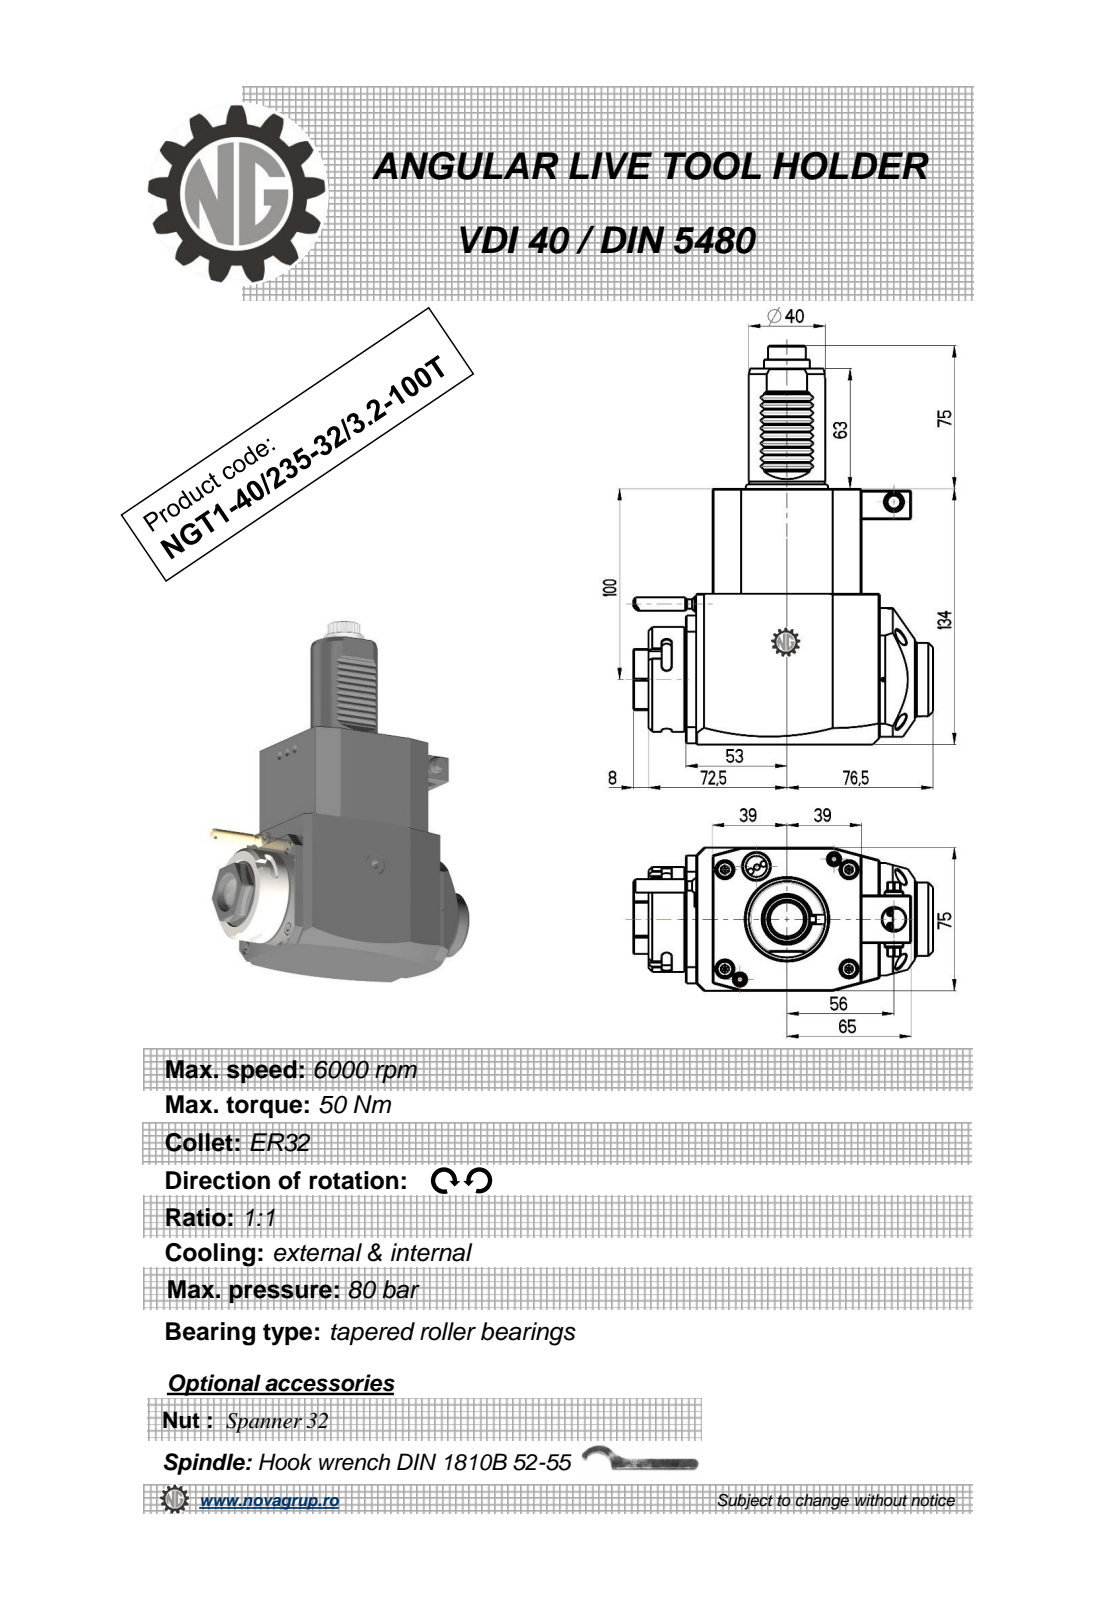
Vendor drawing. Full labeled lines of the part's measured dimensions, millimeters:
Part name (STEP PRODUCT): NGT1_40_235_32_3_2_100T
STEP written by: PRO/ENGINEER BY PARAMETRIC TECHNOLOGY CORPORATION, 2010280 (CONFIG_CONTROL_DESIGN)
Units: millimetres
Bodies: 1 solid, 462 faces (192 planar, 174 cylindrical, 96 other)
Overall size (bounding box): 209 × 157 × 75
Volume: 1 091 000 mm³ · Surface area: 78 751 mm²
Round holes (diameter × count): ⌀2.5 ×1, ⌀3 ×1, ⌀9.5 ×1, ⌀12 ×1, ⌀23 ×1
Round bosses / shafts (diameter × count): ⌀8 ×2, ⌀55 ×1, ⌀48 ×1, ⌀40 ×1, ⌀38.5 ×1, ⌀24 ×1, ⌀10 ×1, ⌀7 ×1
Partial cylindrical surfaces — rounded edges, fillets, slot ends (radius × count): R2.08 ×48, R0.3 ×10, R2.5 ×6, R180 ×2, R3.85 ×1, R4.25 ×1, R9.08 ×1, R9.92 ×1
Main face-to-face distances: 75, 134, 78, 14, 92, 79, 25, 84.88, 19.5, 33.5
Hole centre spacings: 43.2, 54.87, 91.5
